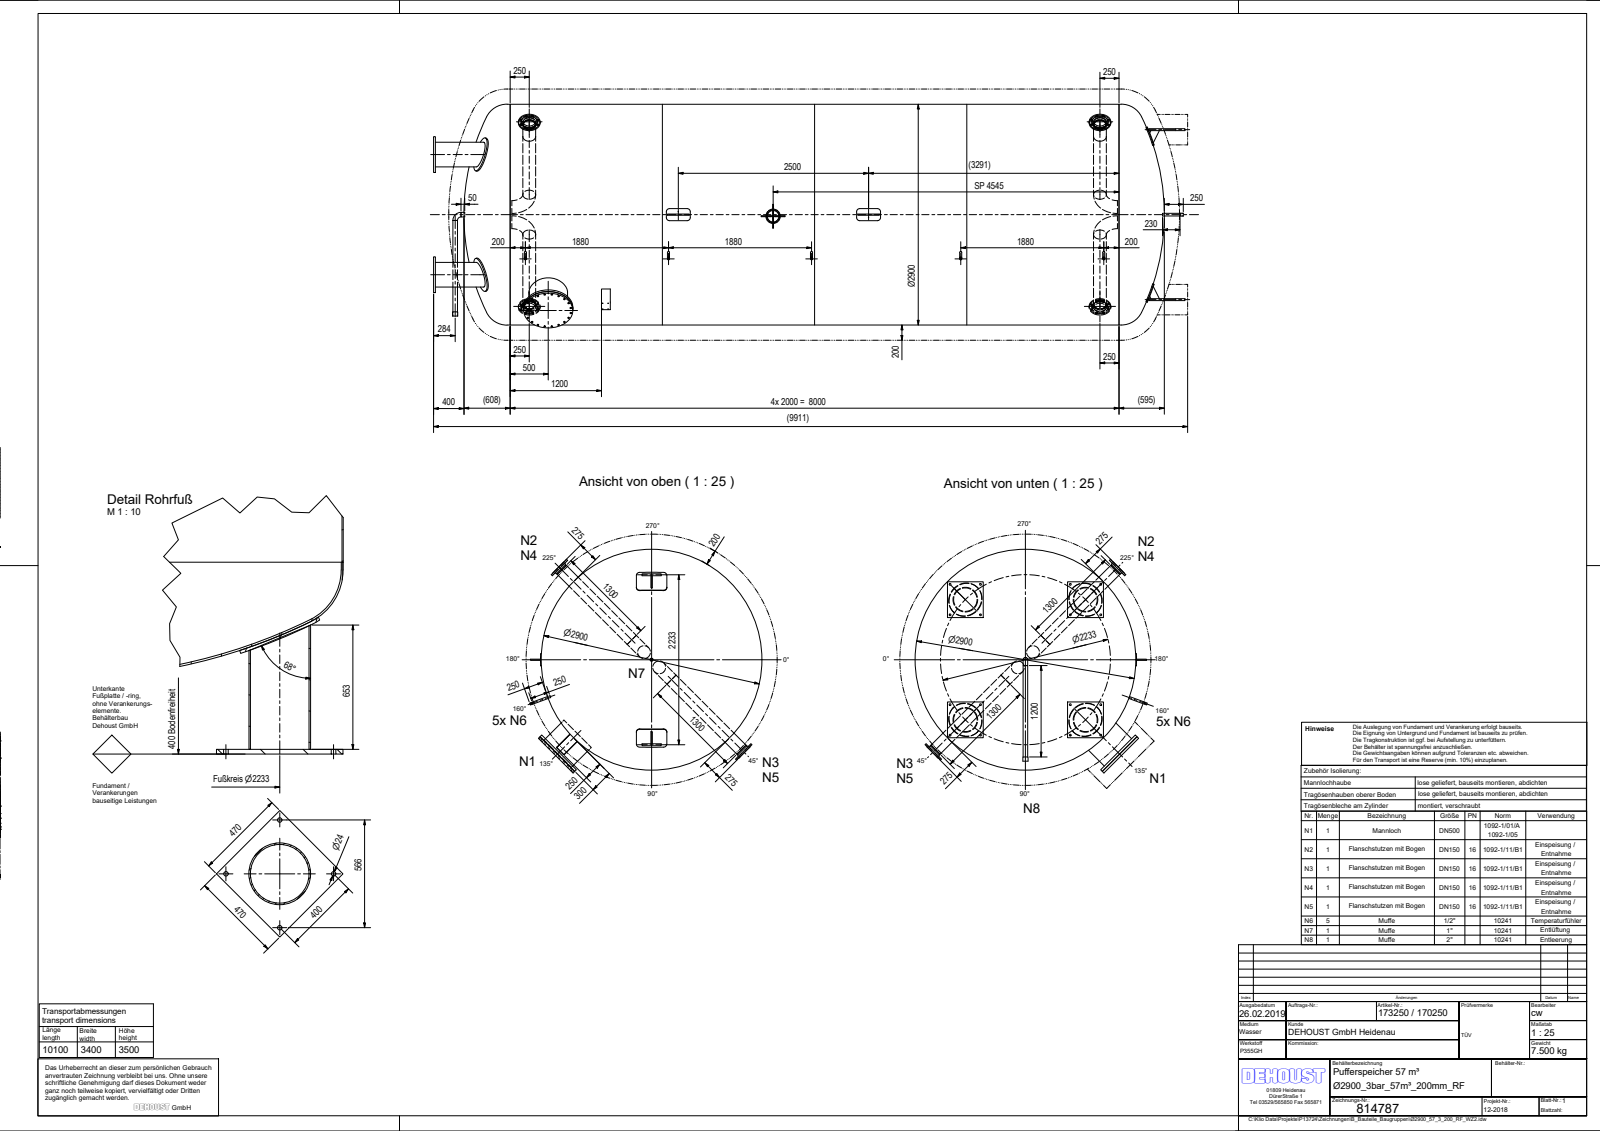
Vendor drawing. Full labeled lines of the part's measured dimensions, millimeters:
Part name (STEP PRODUCT): Ø2900_57_3_200_RF_WZ2; Klöpper_Gew_Ø2900_7,5; Klöpper_Gew_Ø2900_10,3; Zyl_Ø2900_6x8000_2019 (+8 more)
STEP written by: Autodesk Inventor 2019 (AUTOMOTIVE_DESIGN)
Units: millimetres
Bodies: 58 solids, 449 faces (178 planar, 225 cylindrical, 46 other)
Overall size (bounding box): 9874.42 × 3051.99 × 2937.4
Volume: 883 500 000 mm³ · Surface area: 201 700 000 mm²
Round holes (diameter × count): ⌀22 ×64, ⌀24 ×16, ⌀159.3 ×8, ⌀18.63 ×5, ⌀21.7 ×5, ⌀26.9 ×5, ⌀5.8 ×4, ⌀168.3 ×4, ⌀307.9 ×4, ⌀5 ×2, ⌀52.3 ×2, ⌀508 ×2
Round bosses / shafts (diameter × count): ⌀168.3 ×8, ⌀26.9 ×5, ⌀26.4 ×5, ⌀450 ×4, ⌀323.9 ×4, ⌀285 ×4, ⌀212 ×4, ⌀2900 ×1
Partial cylindrical surfaces — rounded edges, fillets, slot ends (radius × count): R42 ×16, R10 ×6, R6 ×4, R5 ×2, R36 ×2, R72 ×2, R125 ×1, R1460 ×1
Main face-to-face distances: 25, 600, 4732.96, 5282.96, 4707.96, 5257.96, 550, 27.99, 3725, 4275
Hole centre spacings: 120, 300, 185.41, 93.86, 7500, 352.67, 169.71, 592.61
